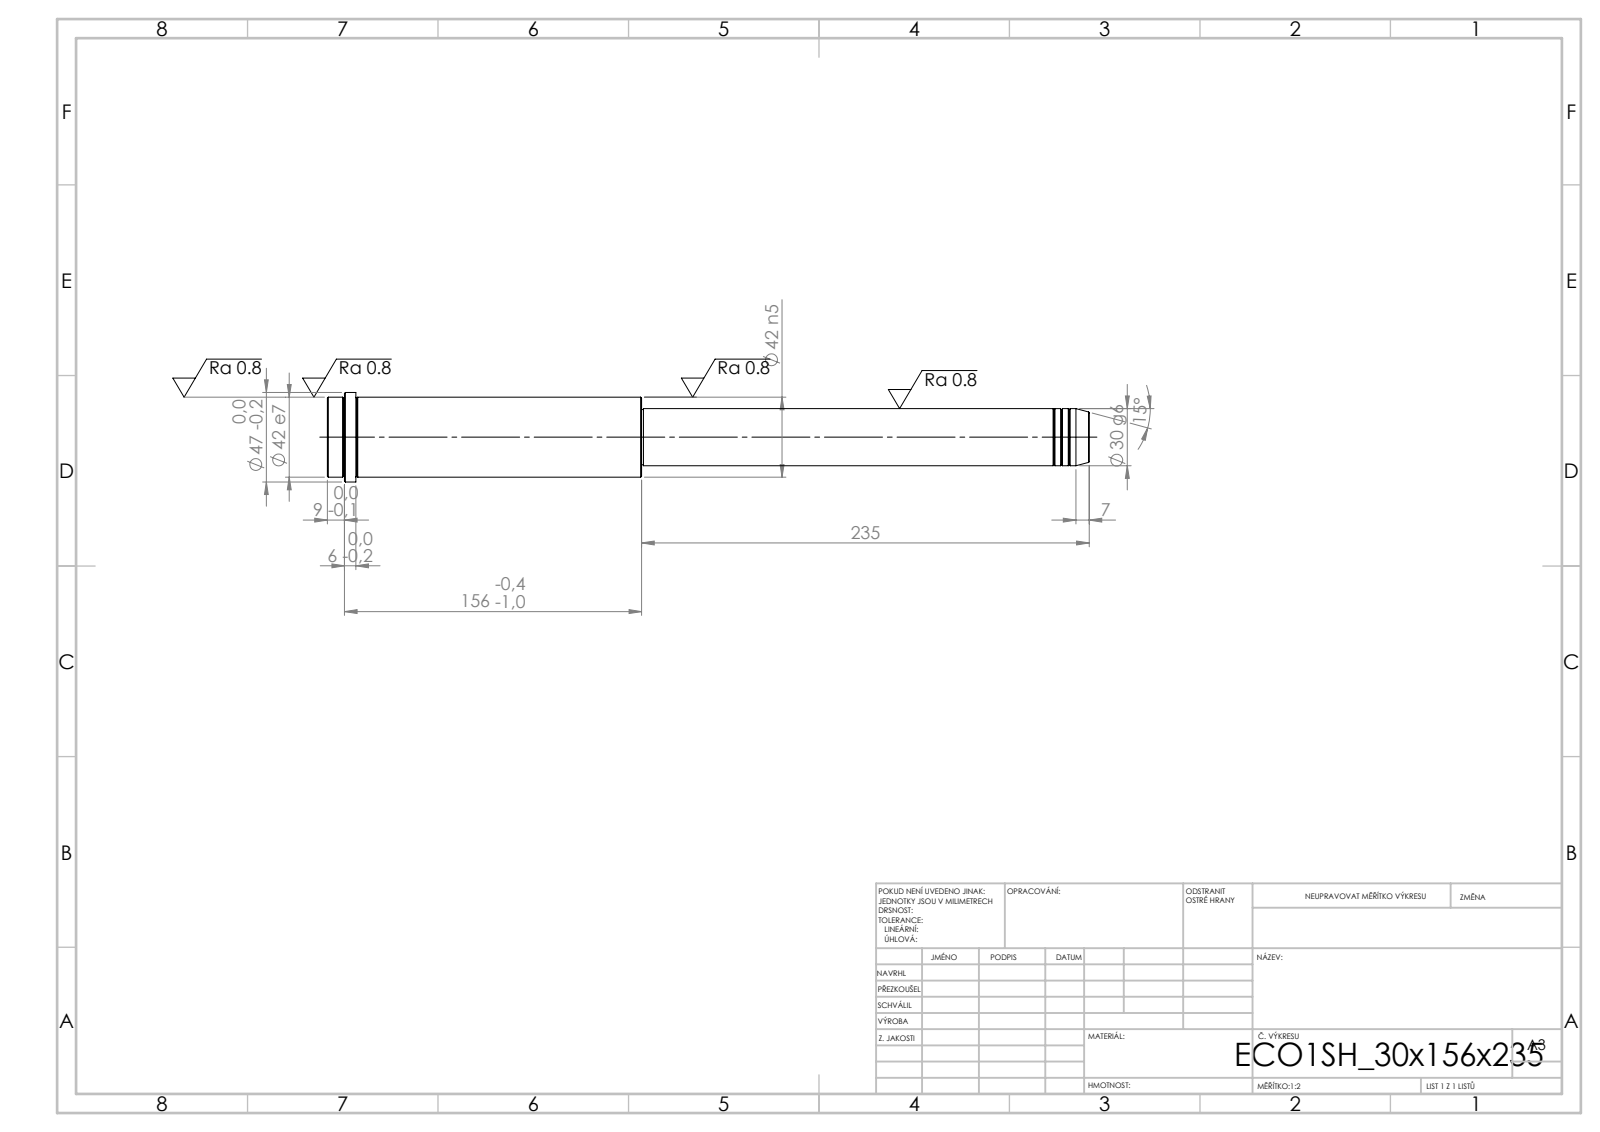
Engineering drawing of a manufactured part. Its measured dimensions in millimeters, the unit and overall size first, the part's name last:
Units: millimetres
Overall size (bounding box): 400 × 47 × 47
Round bosses / shafts (diameter × count): ⌀47 ×1, ⌀42 ×1, ⌀30 ×1, ⌀29 ×1
Main face-to-face distances: 165, 235, 400, 385, 150, 15, 391, 156, 6, 9
Volume: 395 902 mm³ · Surface area: 47 553 mm²
Bodies: 1 solid, 52 faces (6 planar, 16 cylindrical, 30 other)
STEP written by: SolidWorks 2019 (CONFIG_CONTROL_DESIGN)
